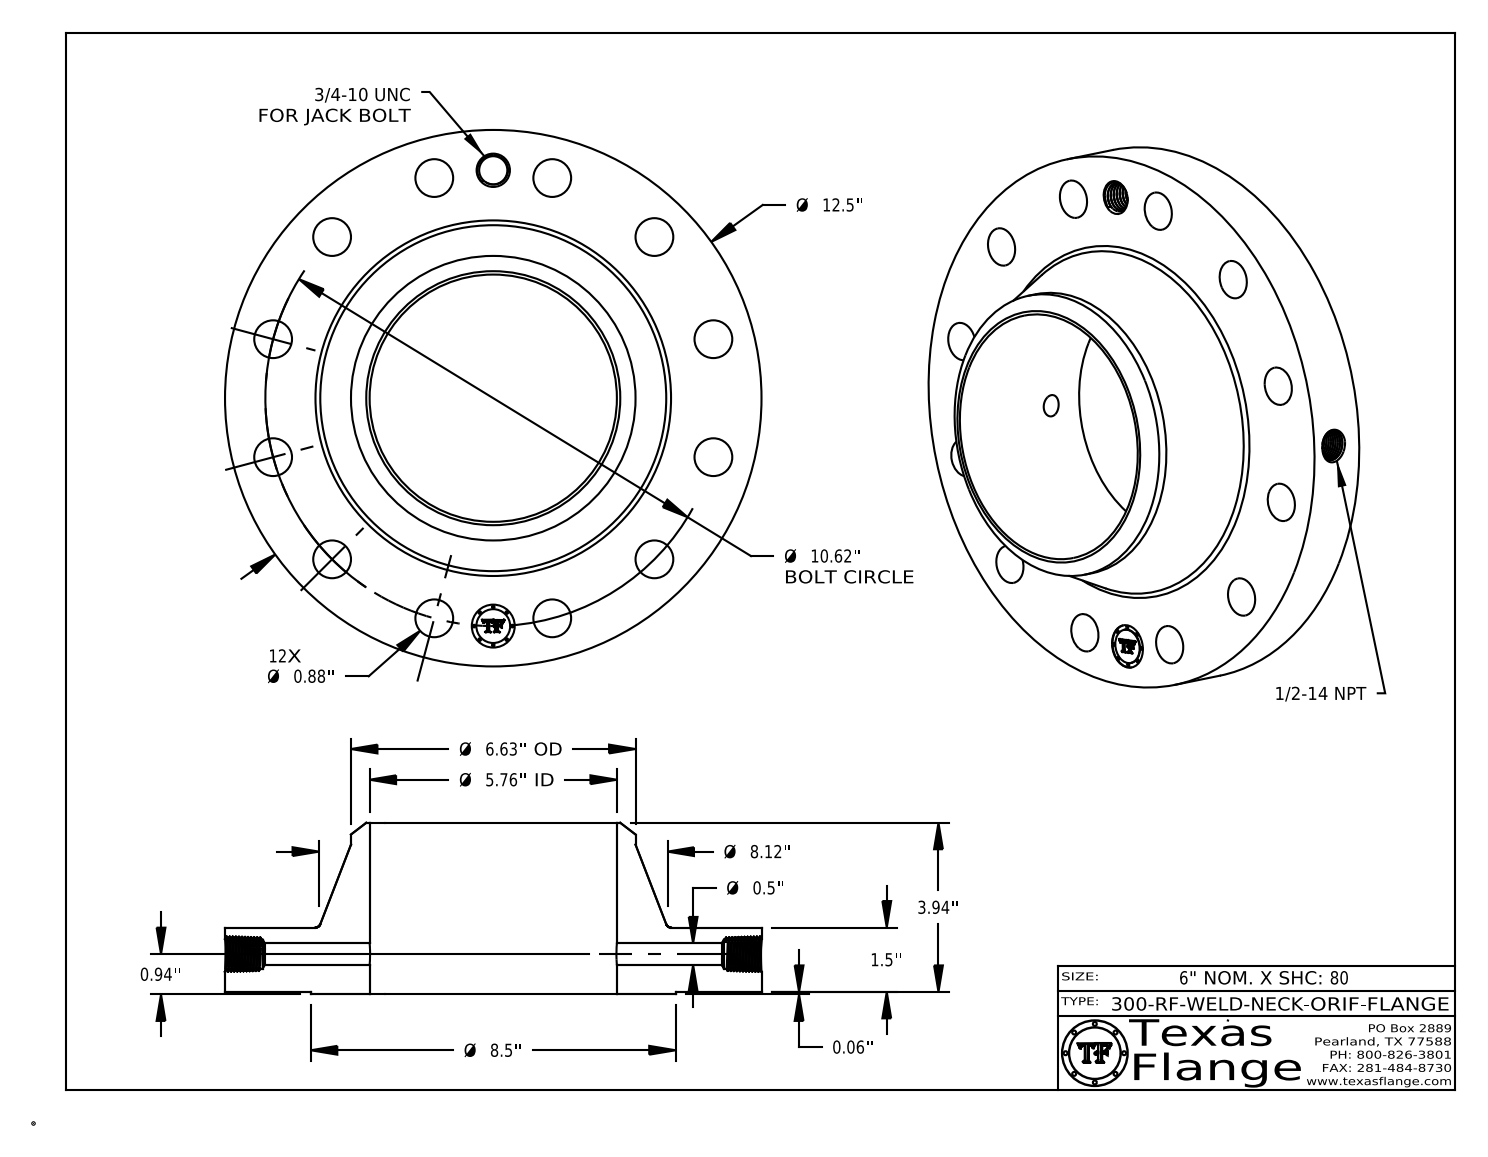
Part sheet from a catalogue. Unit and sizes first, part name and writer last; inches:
Units: inches
Overall size (bounding box): 12.5 × 12.5 × 4
Round holes (diameter × count): ⌀0.88 ×12, ⌀0.5 ×1, ⌀0.656 ×1, ⌀0.672 ×1, ⌀1 ×1, ⌀5.761 ×1
Round bosses / shafts (diameter × count): ⌀0.061 ×8, ⌀12.5 ×1, ⌀8.5 ×1, ⌀6.63 ×1, ⌀0.788 ×1
Main face-to-face distances: 1.5, 0.06, 1.56, 4, 3.94, 2.44, 0.015, 1.545, 1.485, 2.455
Hole centre spacings: 5.31, 7.509, 9.197, 10.258, 5.31, 2.748, 10.62, 1.386
Volume: 169.3 in³ · Surface area: 416.1 in²
Bodies: 1 solid, 773 faces (369 planar, 100 cylindrical, 304 other)
Part name (STEP PRODUCT): 300-RF-WELD-NECK
STEP written by: CATIA V5 STEP AP214 (AUTOMOTIVE_DESIGN)
